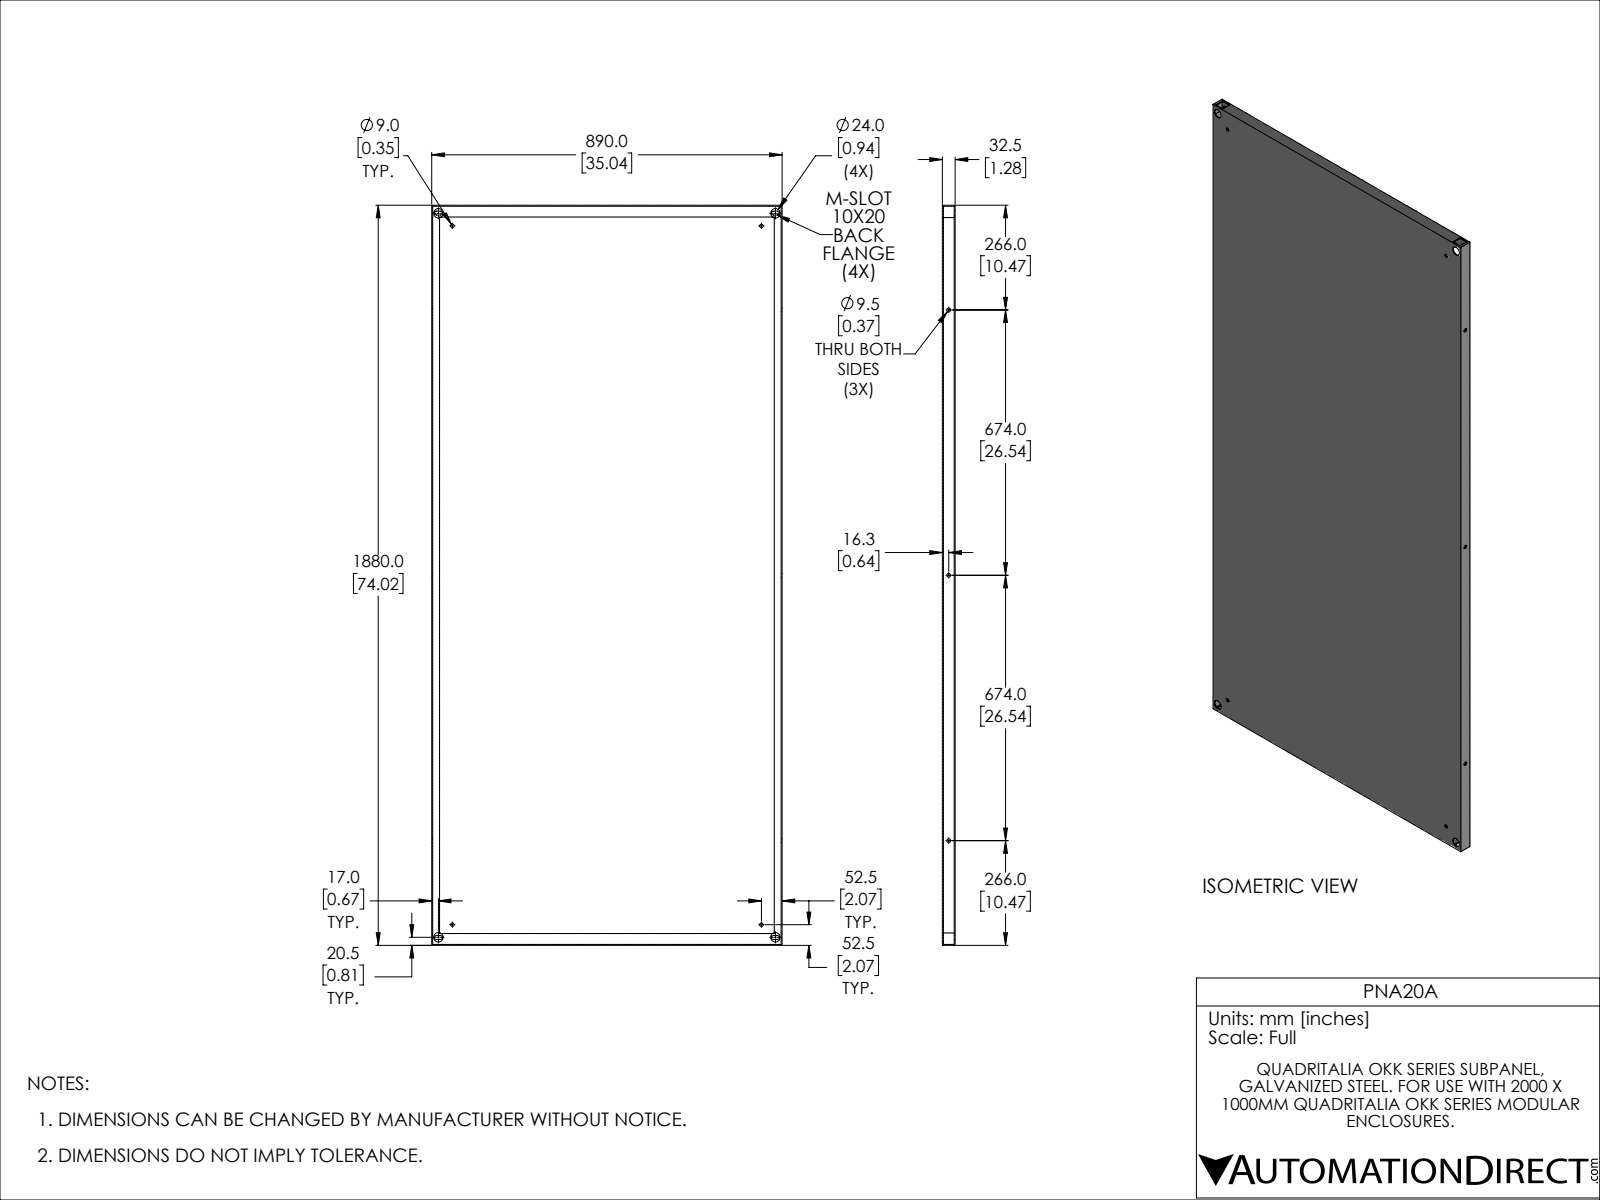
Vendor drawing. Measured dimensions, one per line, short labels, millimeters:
name: PNA20A
written by: SolidWorks 2021 (CONFIG_CONTROL_DESIGN)
unit: mm
bodies: 1 solid, 70 faces (48 planar, 22 cylindrical, 0 other)
size: 1880 × 890 × 32.5
volume: 4 864 000 mm³; area: 3 908 000 mm²
holes: 4× ⌀9, 4× ⌀24, 3× ⌀9.5
rounds: 8× R5
face distances: 2.5, 30, 32.5, 27.5, 887.5, 890, 885, 1877.5, 1880, 1875
hole spacings: 47.8, 821.1, 1807.4, 1984.6, 674, 785, 856, 1775
